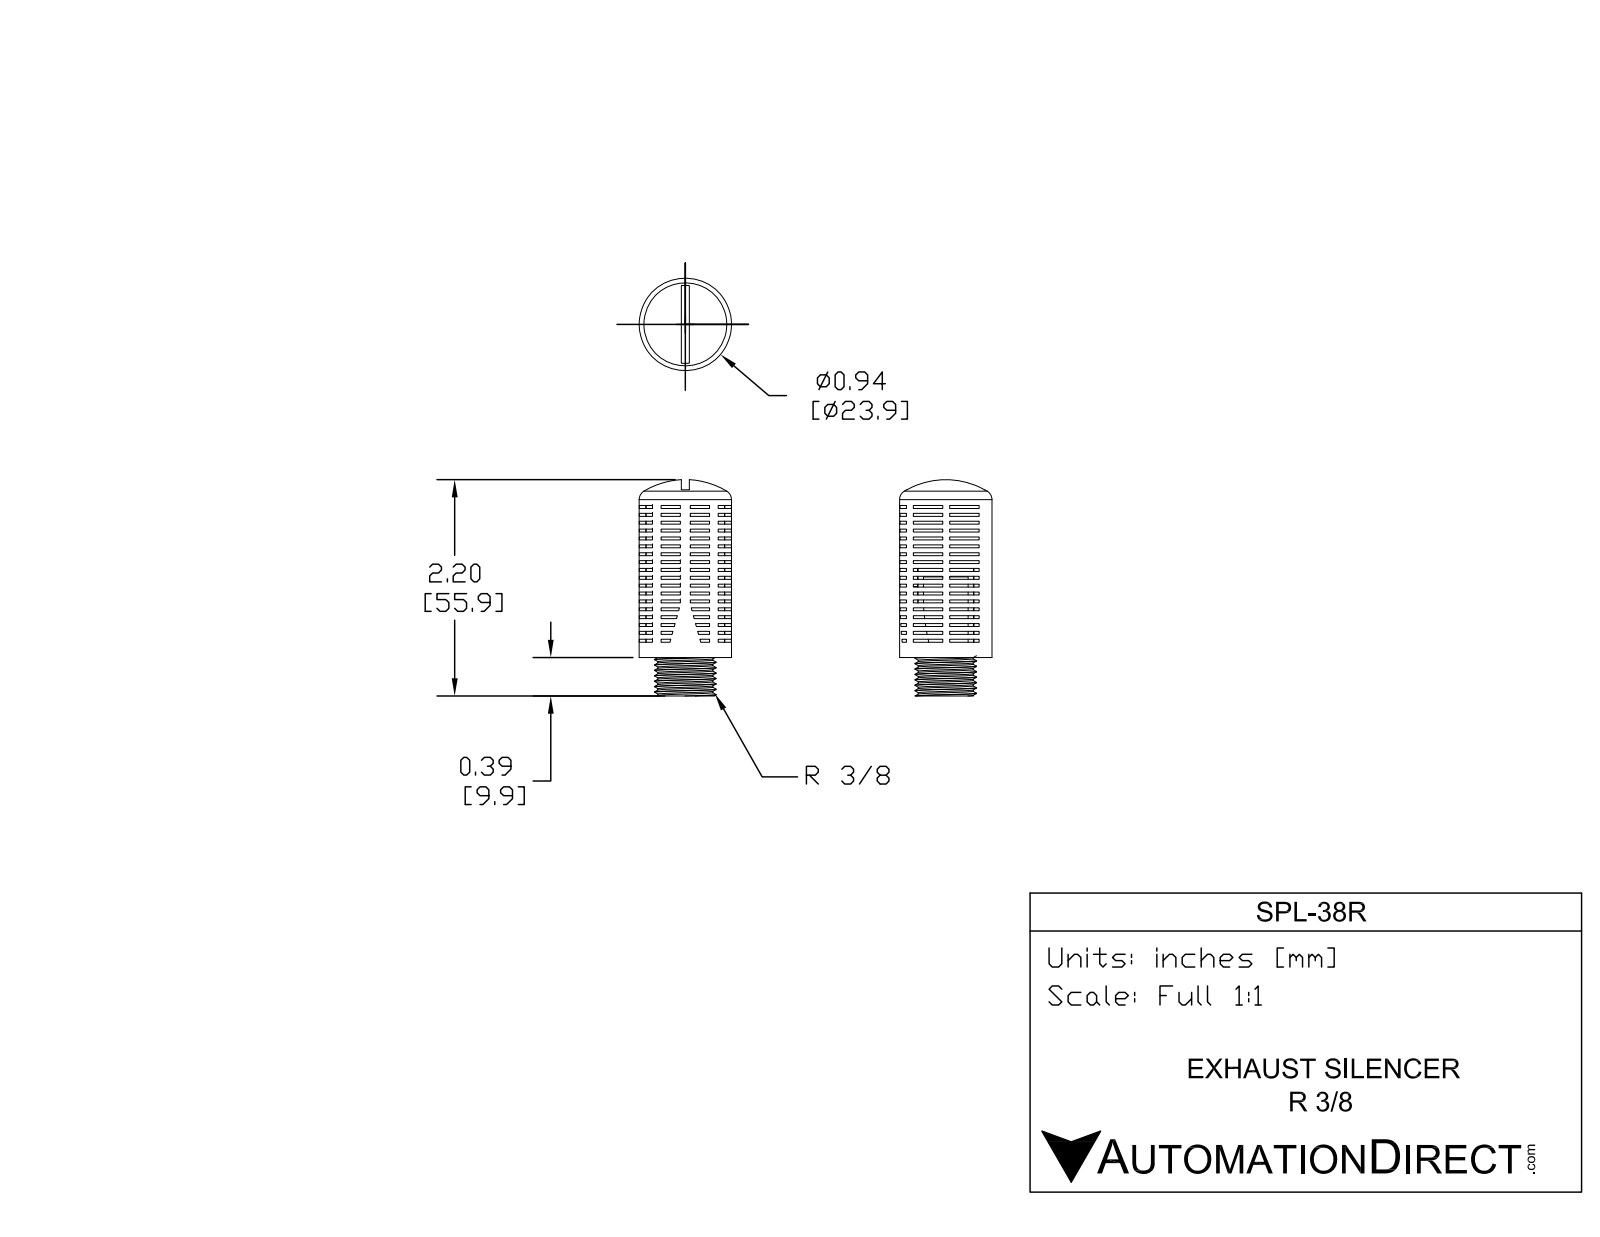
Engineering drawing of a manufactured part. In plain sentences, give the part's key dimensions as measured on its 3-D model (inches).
The part is named "SPL-38R". Its 3-D file was written by "SolidWorks 2015 (CONFIG_CONTROL_DESIGN)". It is 1 solid with 626 faces: 595 planar, 24 cylindrical and 7 other. Overall it measures 2.239 by 0.94 by 0.94 inches. Its volume is 0.473 cubic inches and its surface area 19.9 square inches. Round holes: 1 of diameter 0.465, 1 of diameter 0.803. Round bosses or shafts: 1 of diameter 0.94, 1 of diameter 0.625, 1 of diameter 0.574. The main face-to-face distances are 0.08, 0.05, 0.03, 0.16, 0.16, 0.24, 0.32, 0.4, 0.13, 0.24.
